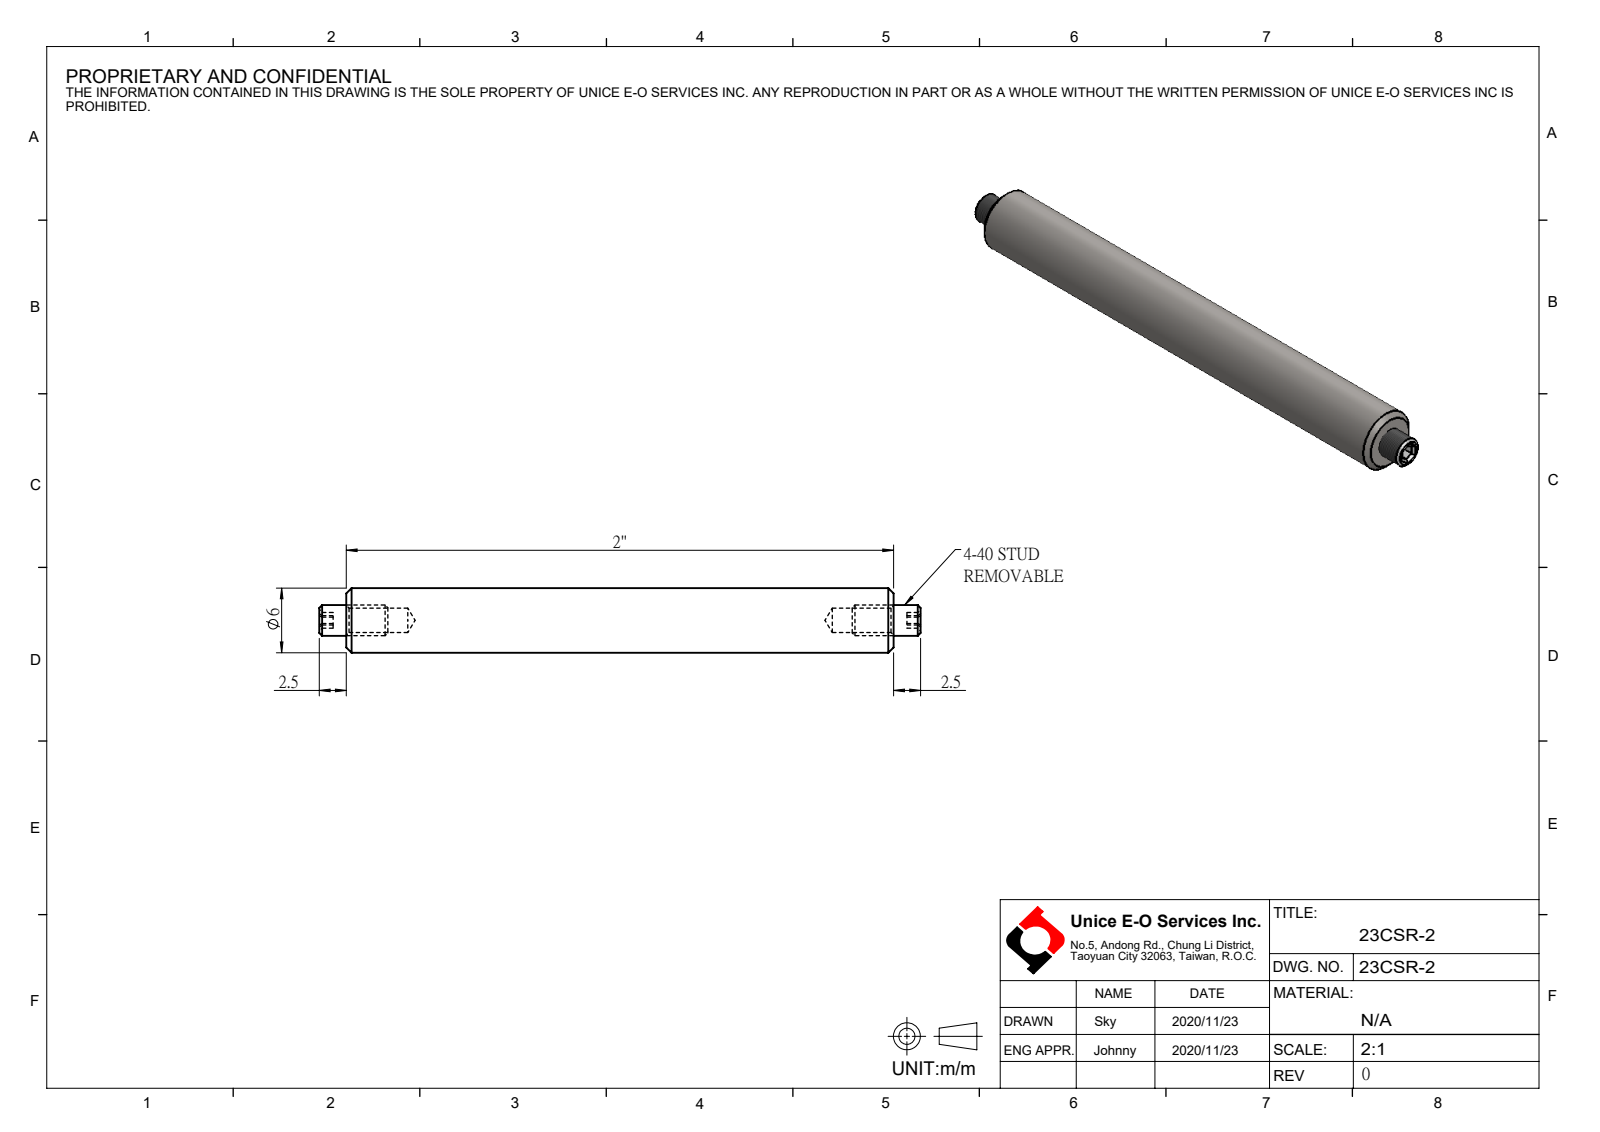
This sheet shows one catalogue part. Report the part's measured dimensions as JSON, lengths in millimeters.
{"part_name": "23CSR-2", "step_written_by": "SolidWorks 2016 (AUTOMOTIVE_DESIGN)", "units": "millimeters", "bodies": {"solids": 0, "faces": 42, "planar": 28, "cylindrical": 6, "other": 8}, "overall_size": [55.8, 6, 6], "round_bosses_or_shafts": [[6, 1], [2.84, 1]], "face_to_face_distances": [50.8, 1.27, 2.5, 53.3, 55.8]}
